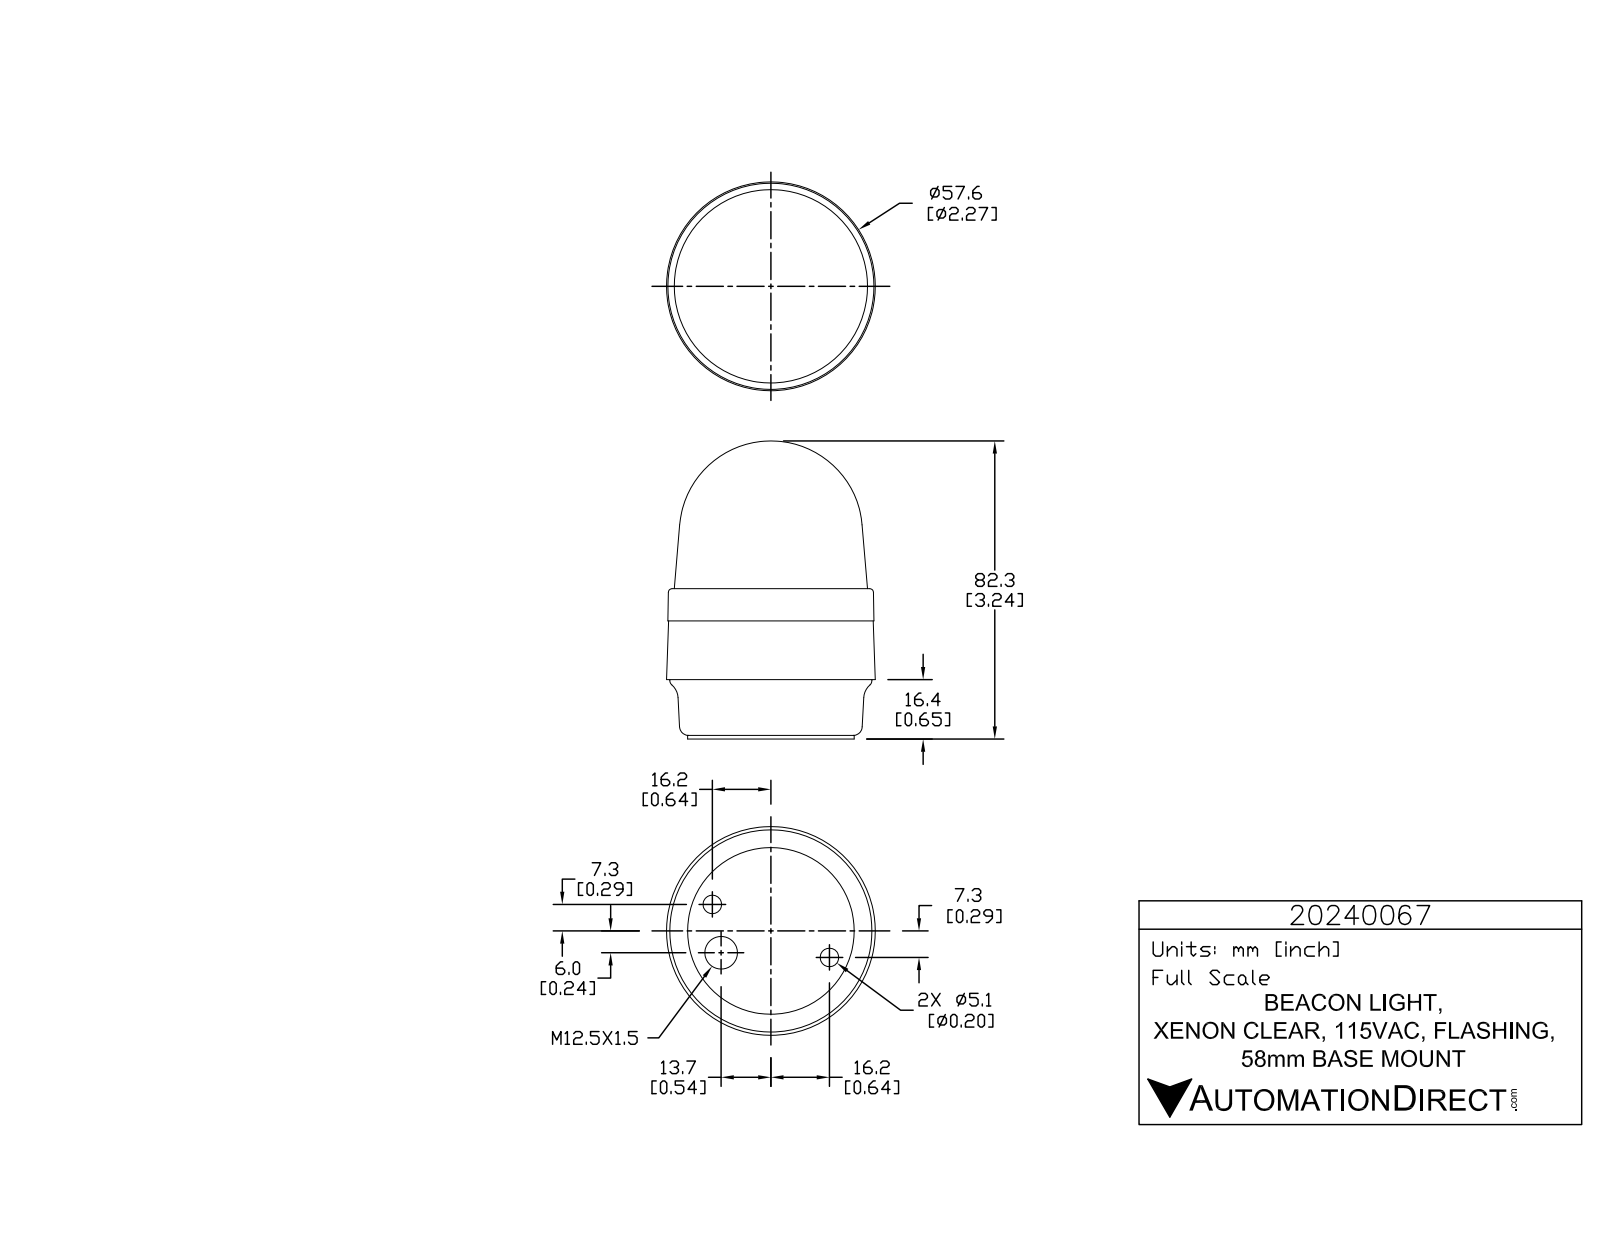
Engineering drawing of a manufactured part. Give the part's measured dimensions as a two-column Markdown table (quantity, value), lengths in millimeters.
| quantity | value |
| --- | --- |
| part name | 20240067 |
| STEP written by | SolidWorks 2015 (AUTOMOTIVE_DESIGN) |
| units | millimeters |
| bodies | 1 solid, 763 faces (527 planar, 145 cylindrical, 91 other) |
| overall size | 82.3 × 57.63 × 57.63 |
| volume | 164 395 mm³ |
| surface area | 16 261 mm² |
| round holes (diameter × count) | 0.99 × 3, 5.11 × 2, 9 × 1 |
| round bosses / shafts (diameter × count) | 5.74 × 3, 1.43 × 3, 55.8 × 1, 46 × 1 |
| partial cylindrical surfaces (radius × count) | 0.2 × 6, 0.21 × 6, 0.21 × 6, 3.32 × 6, 0.1 × 3, 0.12 × 3, 0.19 × 3, 0.2 × 3 |
| main face-to-face distances | 16.4, 1, 15.4, 41.5, 40.5, 25.1, 32.6, 31.6, 16.2, 8.9 |
| hole center spacings | 13.56, 29.94, 35.5 |
